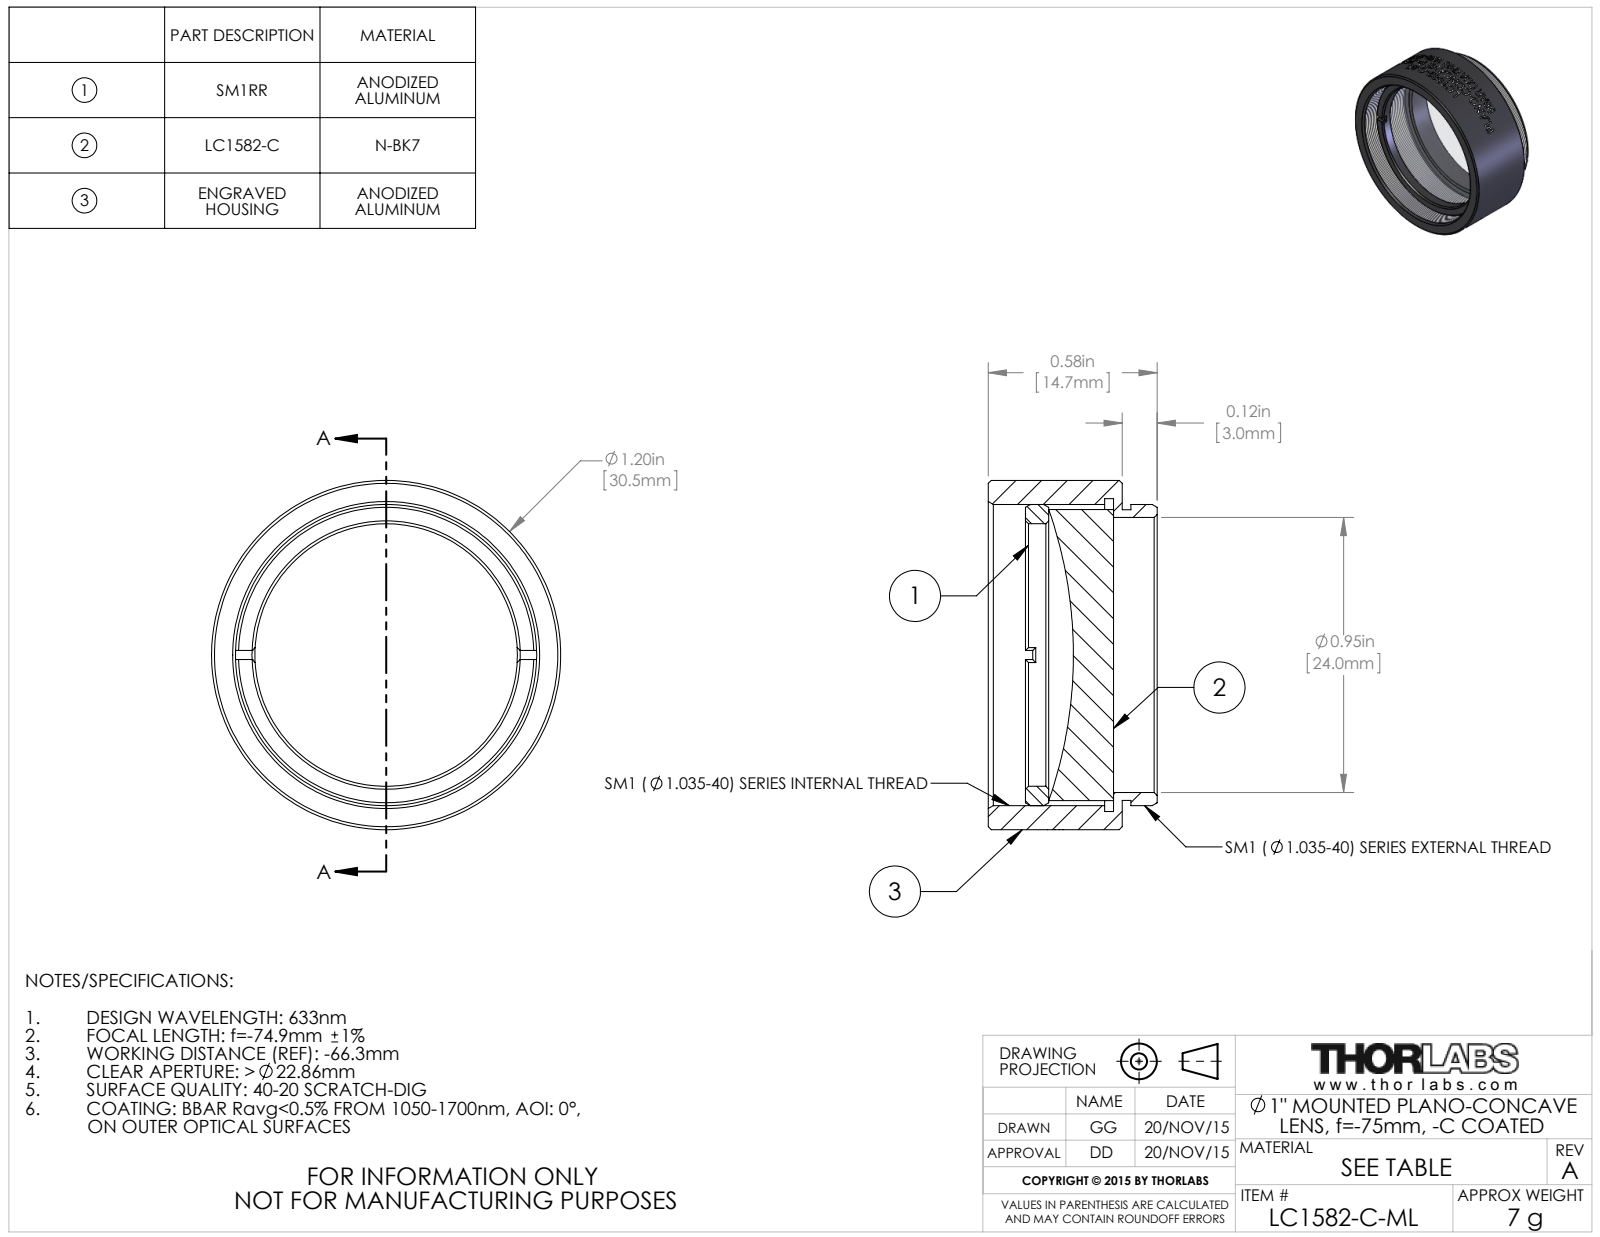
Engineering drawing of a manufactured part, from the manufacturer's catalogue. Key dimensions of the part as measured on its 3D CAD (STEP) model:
Part name (STEP PRODUCT): TTN045307-E0W
STEP written by: SolidWorks 2014 (CONFIG_CONTROL_DESIGN)
Units: inches
Bodies: 3 solids, 152 faces (20 planar, 108 cylindrical, 24 other)
Overall size (bounding box): 1.2 × 1.2 × 0.58
Volume: 0.306 in³ · Surface area: 8.071 in²
Round holes (diameter × count): ⌀0.902 ×1, ⌀0.945 ×1, ⌀1.075 ×1
Round bosses / shafts (diameter × count): ⌀1.2 ×1, ⌀1.035 ×1, ⌀1 ×1, ⌀0.999 ×1
Main face-to-face distances: 0.03, 0.46, 0.43, 0.252, 0.222, 0.208, 0.333, 0.303, 0.08, 0.128
